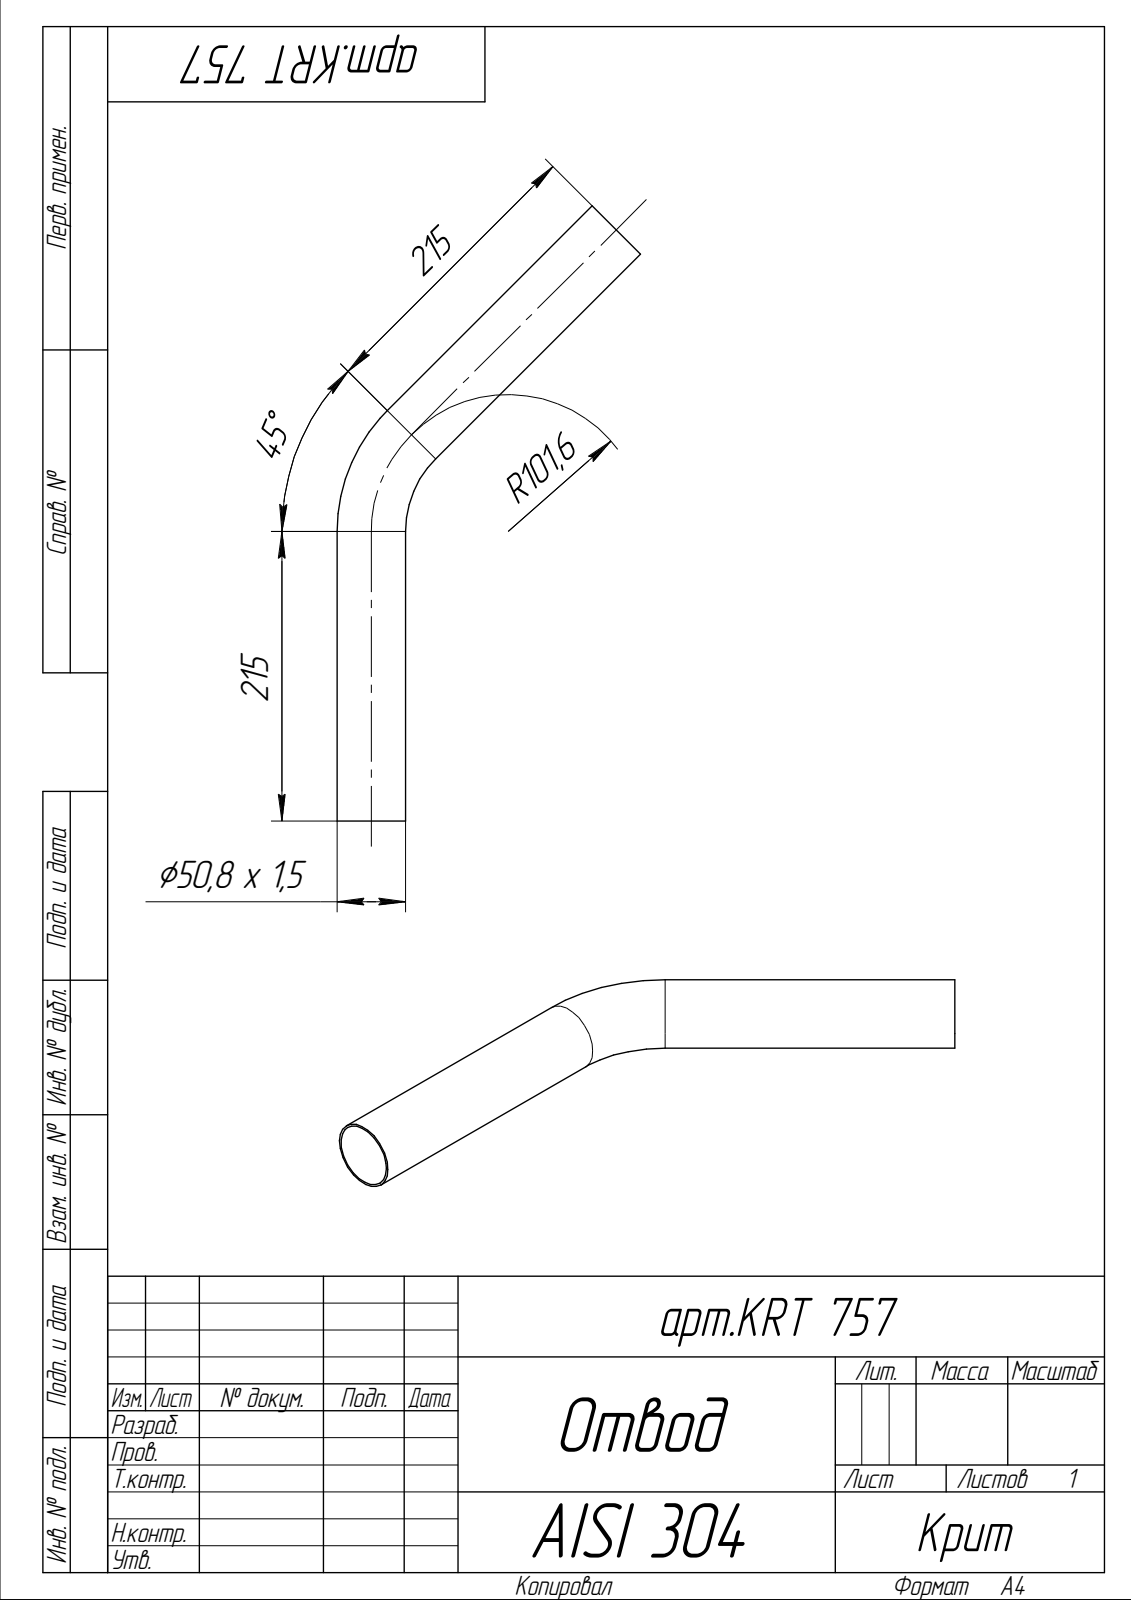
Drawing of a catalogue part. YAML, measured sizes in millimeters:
part_name: "Деталь"
step_written_by: "ASCON Math Kernel (AUTOMOTIVE_DESIGN)"
units: millimeters
bodies: {solids: 1, faces: 8, planar: 2, cylindrical: 4, other: 2}
overall_size: [456.83, 225.15, 50.8]
volume: 118436
surface_area: 158380
round_holes:
  - {diameter: 47.8, count: 2}
round_bosses_or_shafts:
  - {diameter: 50.8, count: 2}
